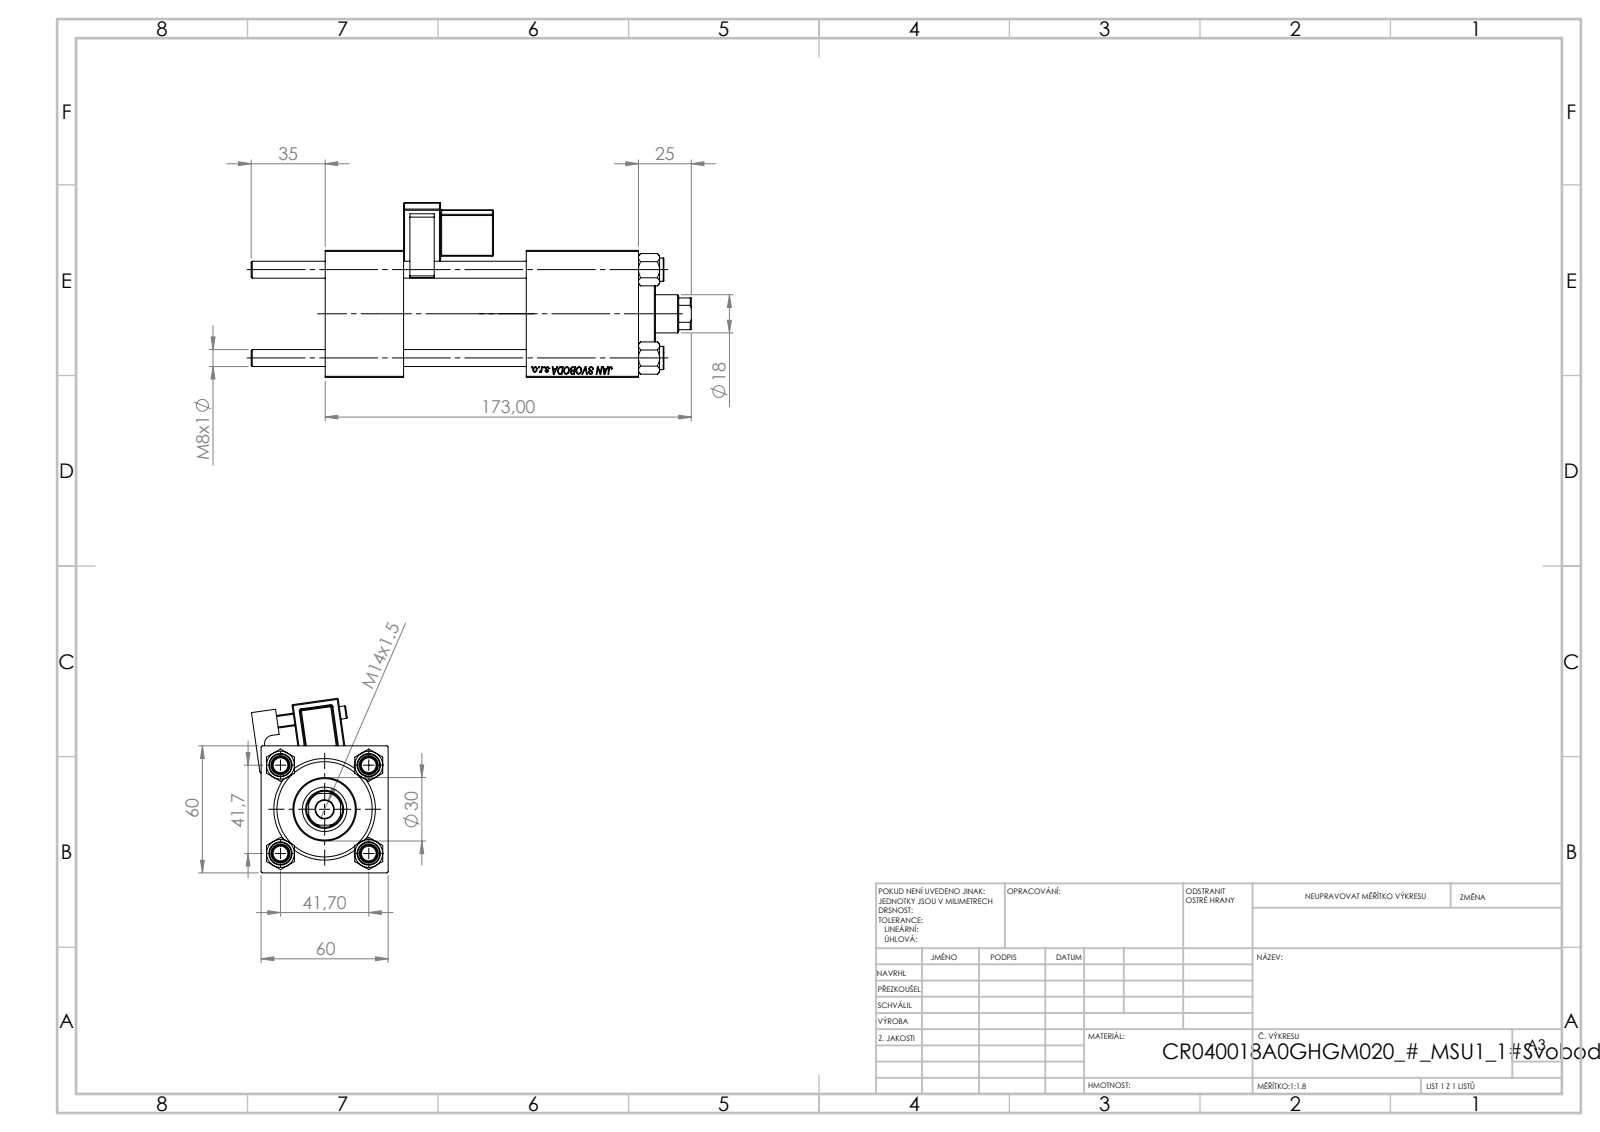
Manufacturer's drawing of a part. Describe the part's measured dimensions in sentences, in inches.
The part is named "V215CR_MSU; V215CR_BODY_A; V215CR_VCP; NUT_M5 (+2 more)". Its 3-D file was written by "SolidWorks 2019 (CONFIG_CONTROL_DESIGN)". It is 12 solids with 1212 faces: 550 planar, 108 cylindrical and 554 other. Overall it measures 8.189 by 3.244 by 2.543 inches. Its volume is 26.5 cubic inches and its surface area 186.1 square inches. Round holes: 4 of diameter 0.315, 2 of diameter 0.276, 2 of diameter 0.656, 2 of diameter 0.945, 1 of diameter 0.335, 1 of diameter 0.709, 1 of diameter 0.827, 1 of diameter 1.22, 1 of diameter 1.575, 1 of diameter 1.772. Round bosses or shafts: 4 of diameter 0.433, 1 of diameter 1.811, 1 of diameter 1.181, 1 of diameter 0.236. Partial cylindrical surfaces (rounded edges, fillets, slot ends): 24 of radius 0.02, 1 of radius 0.039, 1 of radius 0.098, 1 of radius 0.157, 1 of radius 0.335. The main face-to-face distances are 2.362, 1.457, 5.827, 4.37, 2.283, 2.087, 3.74, 4.697, 3.24, 0.957. The hole center spacings are 1.161, 1.642, 2.322, 3.642.
